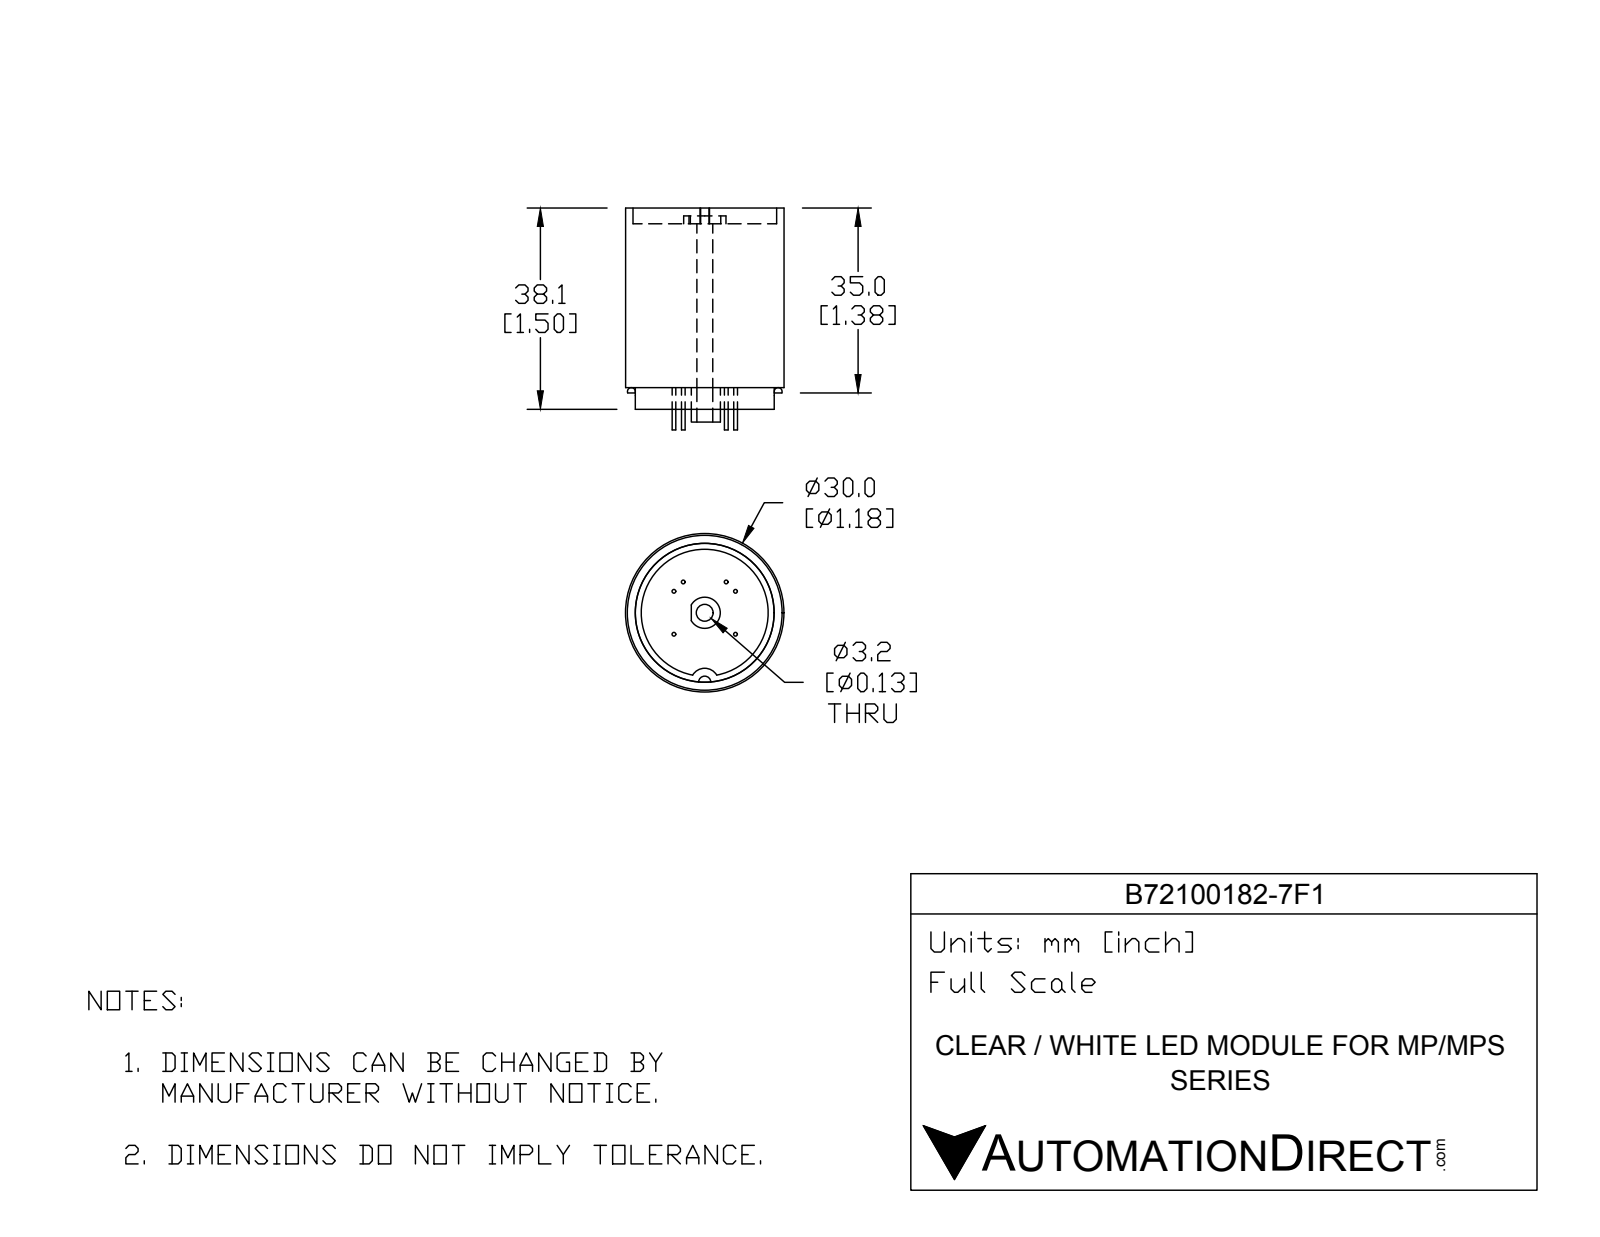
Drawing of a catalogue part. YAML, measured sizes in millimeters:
part_name: "B72100182-7F1"
step_written_by: "SolidWorks 2016 (AUTOMOTIVE_DESIGN)"
units: millimeters
bodies: {solids: 10, faces: 64, planar: 25, cylindrical: 35, other: 4}
overall_size: [42, 30, 30]
volume: 22787
surface_area: 6668
round_holes:
  - {diameter: 3, count: 1}
  - {diameter: 6.06, count: 1}
  - {diameter: 24.04, count: 1}
  - {diameter: 27.2, count: 1}
round_bosses_or_shafts:
  - {diameter: 0.7, count: 6}
  - {diameter: 30, count: 1}
  - {diameter: 26.3, count: 1}
  - {diameter: 8, count: 1}
  - {diameter: 5.9, count: 1}
partial_cylinders:
  - {radius: 0.9, count: 1}
  - {radius: 1.15, count: 1}
  - {radius: 2.65, count: 1}
face_to_face_distances: [31, 34, 3, 4.1, 35.1, 38.1, 1.5, 36.6, 32.5, 2.42]
